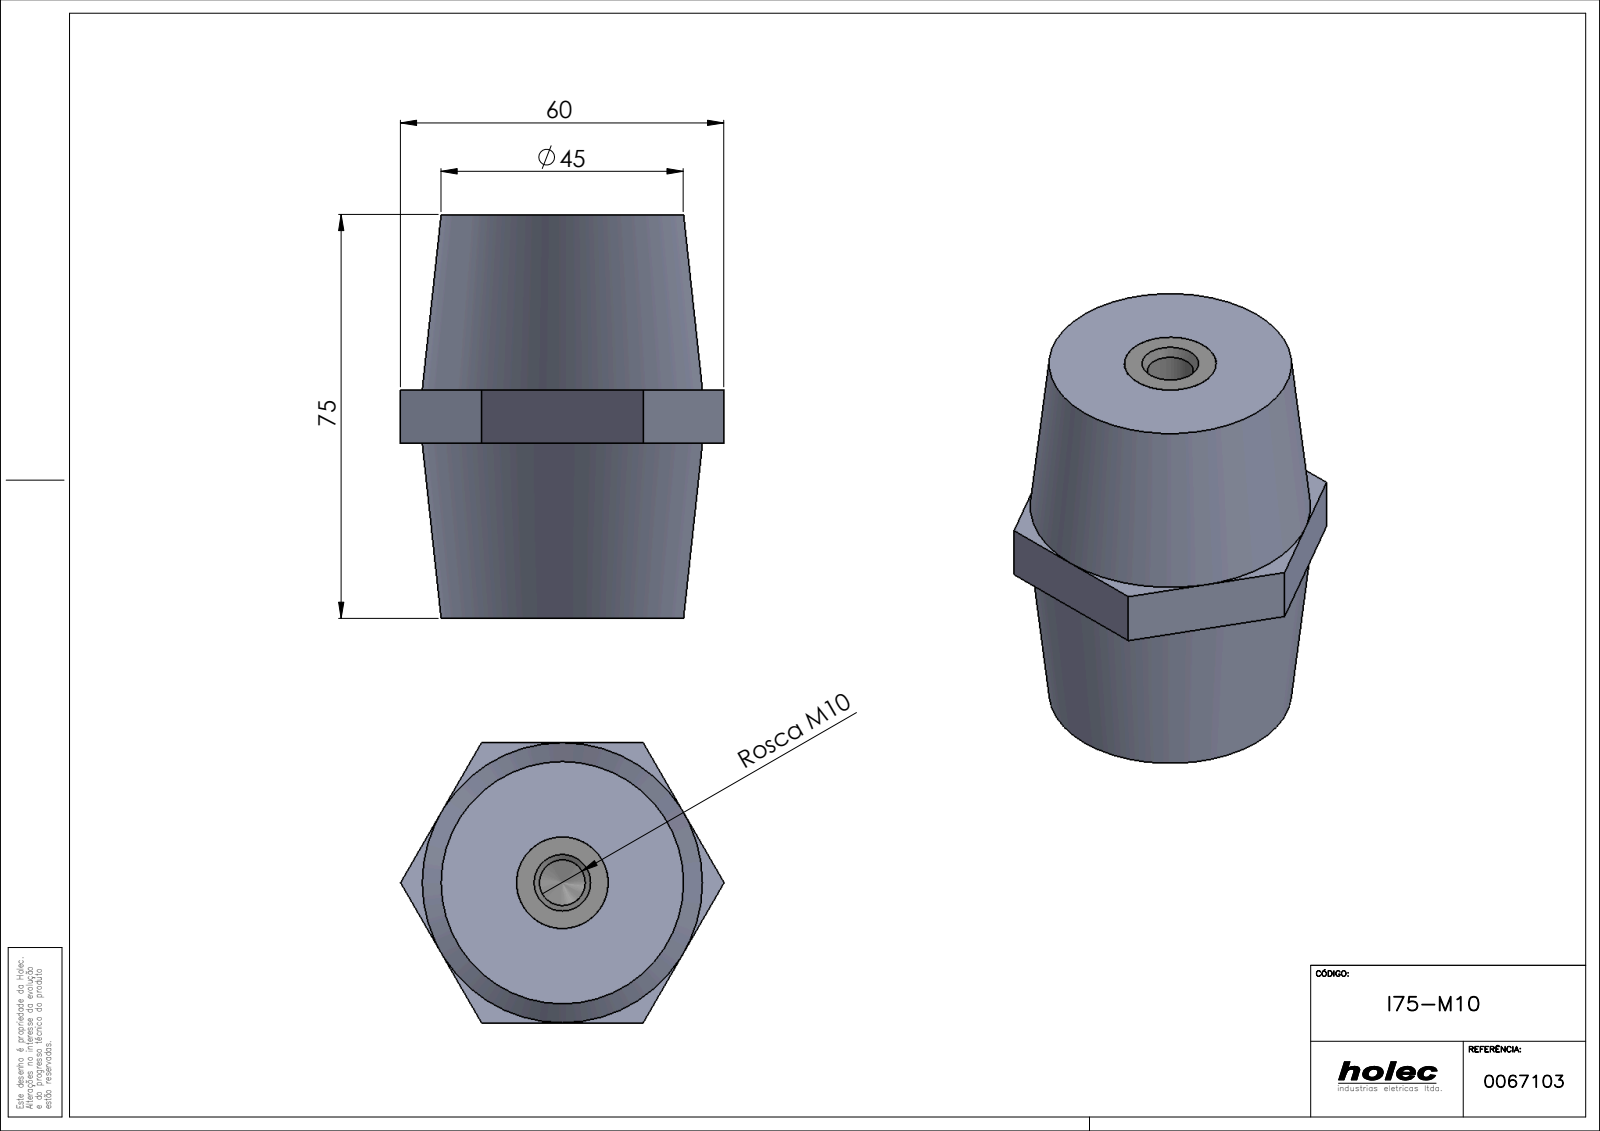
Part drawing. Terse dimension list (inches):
name: PB1_0002; I75-M10; PB1_0109(PB1_0110_10)
written by: SolidWorks 2017 (AUTOMOTIVE_DESIGN)
unit: in
bodies: 3 solids, 162 faces (82 planar, 12 cylindrical, 68 other)
size: 2.953 × 2.364 × 2.047
volume: 8.665 in³; area: 33.21 in²
holes: 1× ⌀0.335, 1× ⌀0.551
face distances: 0.669, 2.953, 2.047, 2.284, 2.283, 0.197, 0.472, 0.669, 1.615, 1.28
